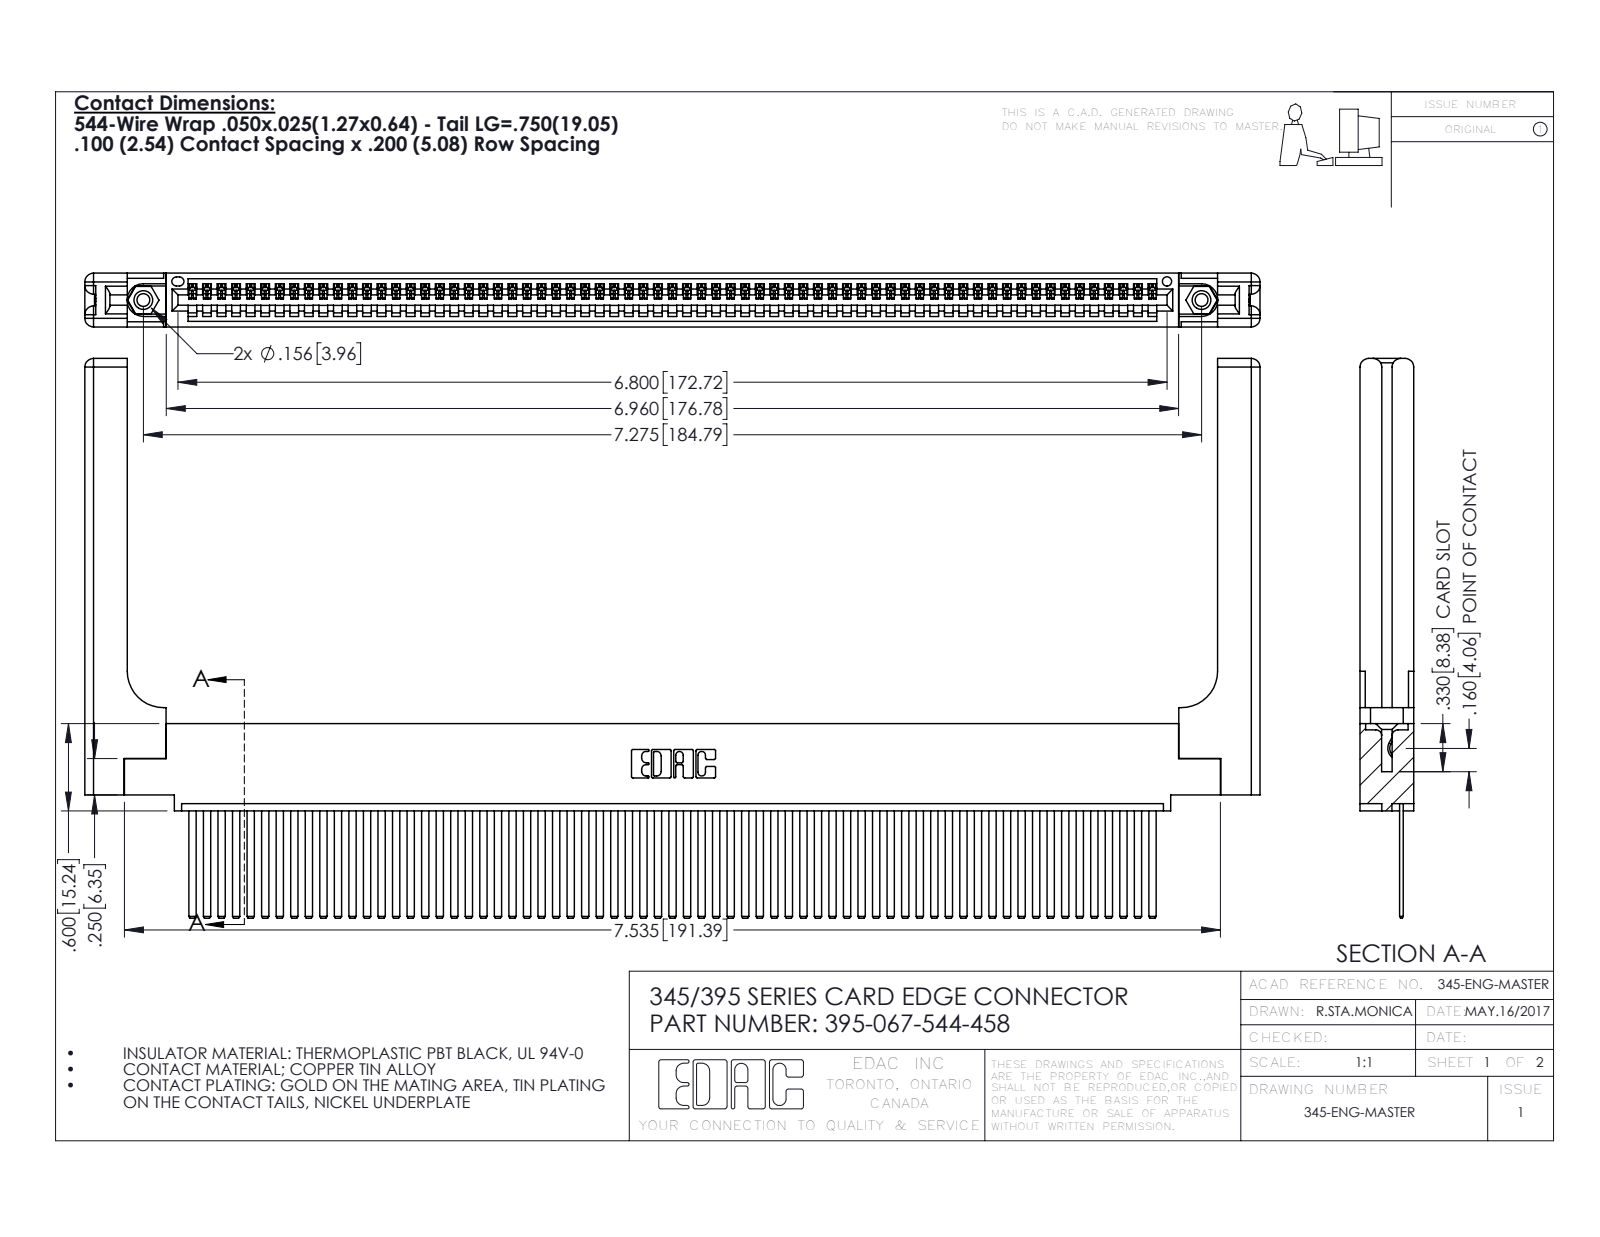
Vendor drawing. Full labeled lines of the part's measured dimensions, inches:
Part name (STEP PRODUCT): 345-220-058_345-220-058; 345 Part_0.110 Offset - 0.156 Dia-TH; 345-292-001_345-293-144; 345-250-001_345-250-001-102 (+1 more)
STEP written by: SolidWorks 2016 (CONFIG_CONTROL_DESIGN)
Units: inches
Bodies: 72 solids, 3870 faces (2644 planar, 1166 cylindrical, 60 other)
Overall size (bounding box): 8.079 × 3.847 × 0.37
Volume: 1.764 in³ · Surface area: 54.5 in²
Round holes (diameter × count): ⌀0.089 ×2, ⌀0.125 ×2, ⌀0.156 ×2, ⌀0.064 ×1
Round bosses / shafts (diameter × count): ⌀0.155 ×2
Partial cylindrical surfaces — rounded edges, fillets, slot ends (radius × count): R0.006 ×134, R0.01 ×22, R0.06 ×16, R0.007 ×6, R0.031 ×6, R0.026 ×3, R0.03 ×2, R0.031 ×2
Main face-to-face distances: 0.072, 0.298, 0.098, 0.272, 0.025, 0.37, 0.2, 0.225, 0.148, 0.15
Hole centre spacings: 0.27, 7.039, 7.275
